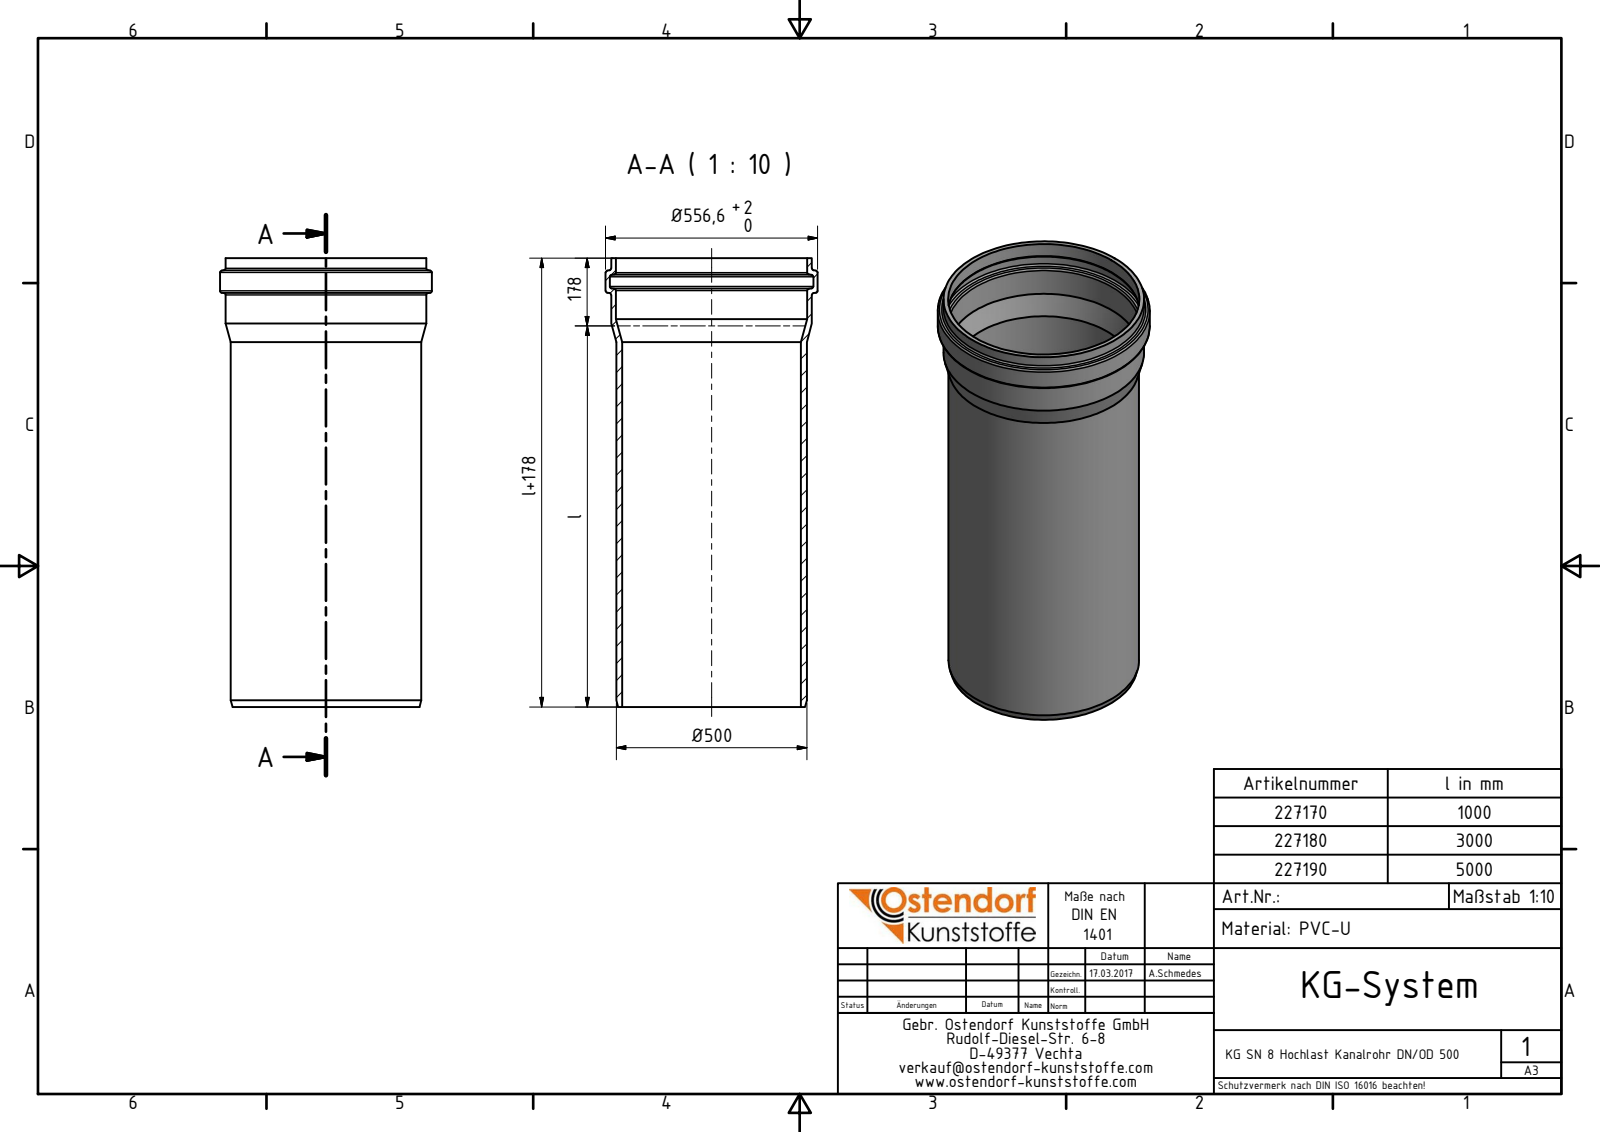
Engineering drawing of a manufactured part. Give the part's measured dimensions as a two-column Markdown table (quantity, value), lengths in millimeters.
| quantity | value |
| --- | --- |
| part name | 227190 KGEM Passlängen SN 8 DN_OD 500x5000 |
| STEP written by | Autodesk Inventor 2016 (AUTOMOTIVE_DESIGN) |
| units | millimeters |
| bodies | 1 solid, 25 faces (2 planar, 8 cylindrical, 15 other) |
| overall size | 5178 × 556.6 × 556.6 |
| volume | 122 200 000 mm³ |
| surface area | 15 940 000 mm² |
| round holes (diameter × count) | 469.5 × 1, 502 × 1, 534.6 × 1 |
| round bosses / shafts (diameter × count) | 556.6 × 1, 526.8 × 1, 500.5 × 1 |
| main face-to-face distances | 5178 |
